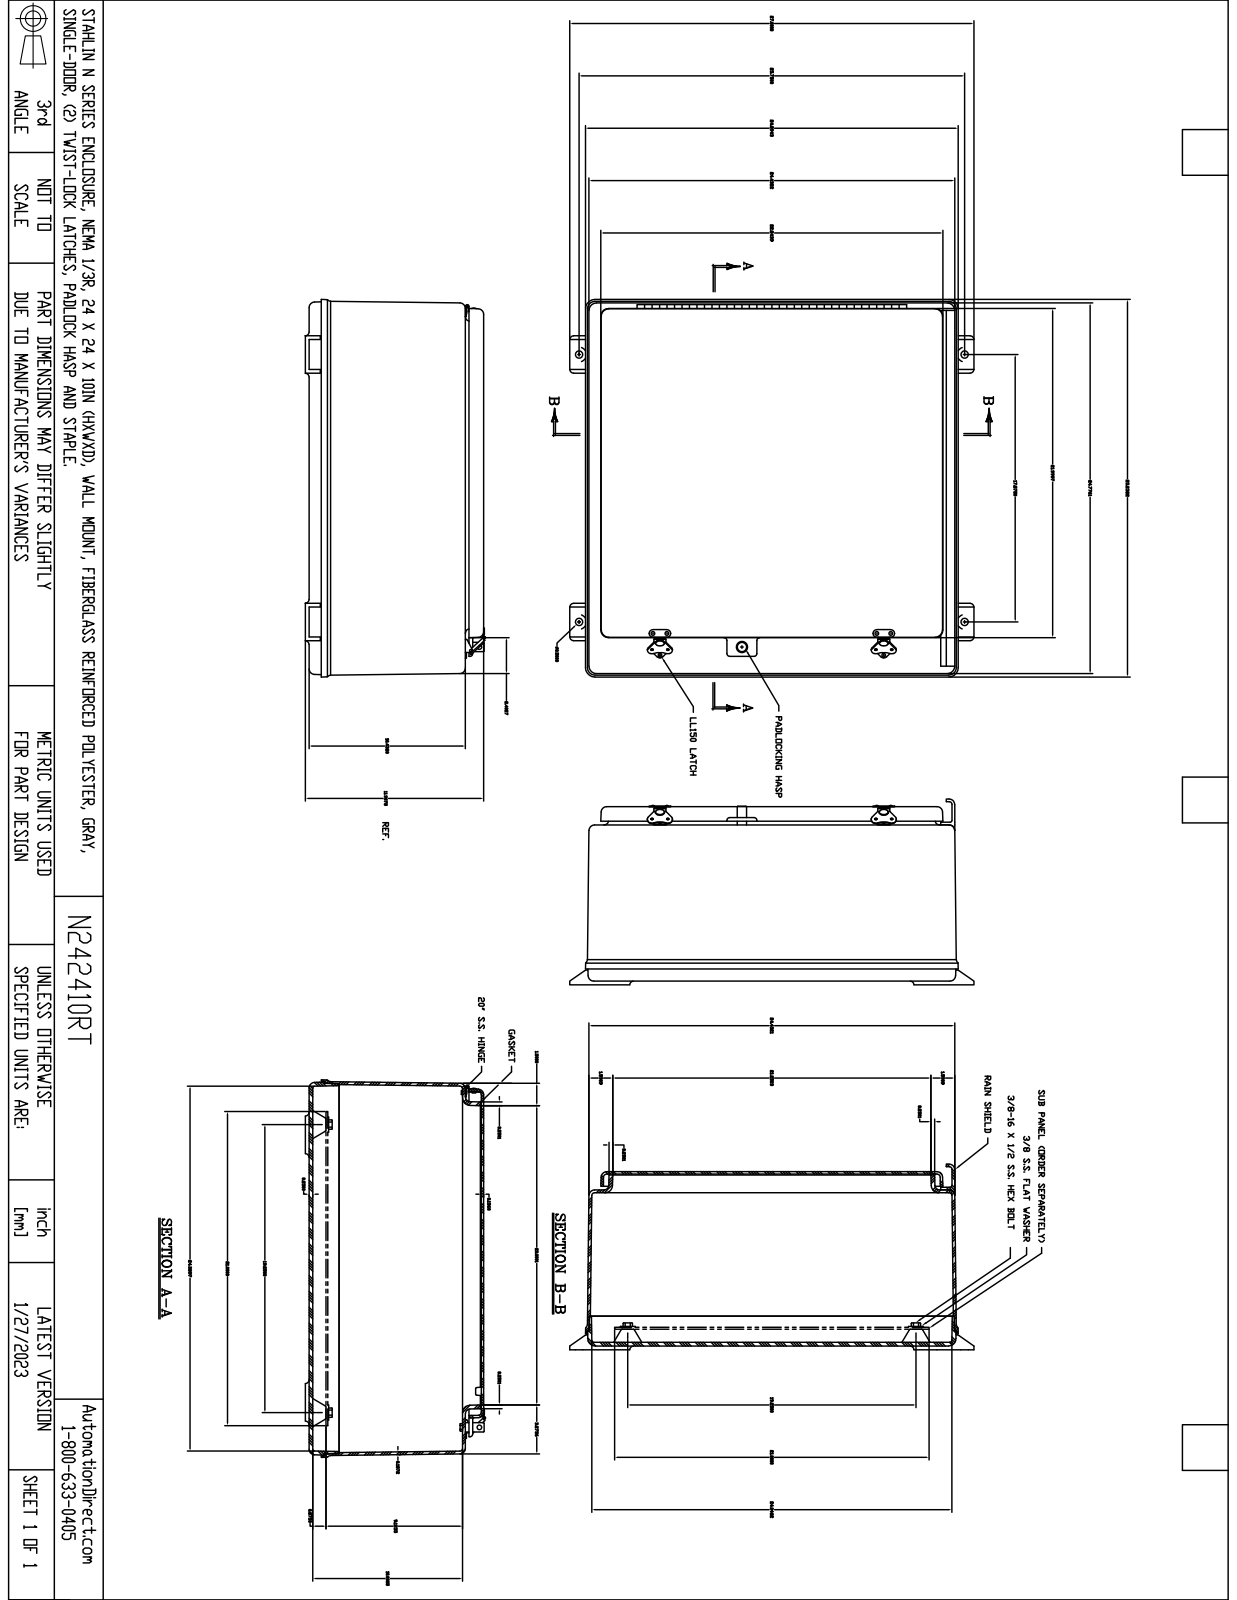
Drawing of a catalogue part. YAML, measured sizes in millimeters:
part_name: "T242410RT"
step_written_by: "SolidWorks 2018 (AUTOMOTIVE_DESIGN)"
units: millimeters
bodies: {solids: 42, faces: 1171, planar: 451, cylindrical: 460, other: 260}
overall_size: [685.8, 641.4, 315.9]
volume: 8461000
surface_area: 3520000
round_holes:
  - {diameter: 3.3, count: 25}
  - {diameter: 1.7, count: 9}
  - {diameter: 1.6, count: 8}
  - {diameter: 3.5, count: 4}
  - {diameter: 4.7, count: 4}
  - {diameter: 7.1, count: 4}
  - {diameter: 14.3, count: 4}
  - {diameter: 1.7, count: 2}
  - {diameter: 3.7, count: 2}
  - {diameter: 13, count: 2}
  - {diameter: 13, count: 2}
  - {diameter: 3.2, count: 1}
round_bosses_or_shafts:
  - {diameter: 7.5, count: 11}
  - {diameter: 3.6, count: 8}
  - {diameter: 12.7, count: 2}
  - {diameter: 6.4, count: 1}
  - {diameter: 5.1, count: 1}
  - {diameter: 5.1, count: 1}
  - {diameter: 3.4, count: 1}
partial_cylinders:
  - {radius: 0.3, count: 60}
  - {radius: 6.4, count: 24}
  - {radius: 4.7, count: 12}
  - {radius: 9.5, count: 12}
  - {radius: 12.7, count: 12}
  - {radius: 4.8, count: 10}
  - {radius: 0.8, count: 8}
  - {radius: 3.2, count: 7}
face_to_face_distances: [4.7, 6.4, 296.1, 289.7, 4, 292.1, 285.8, 265.1, 258.7, 254]
hole_center_spacings: [133.4, 298.5, 165.1, 431.8, 38.4, 84.4, 379.4, 478.6]
